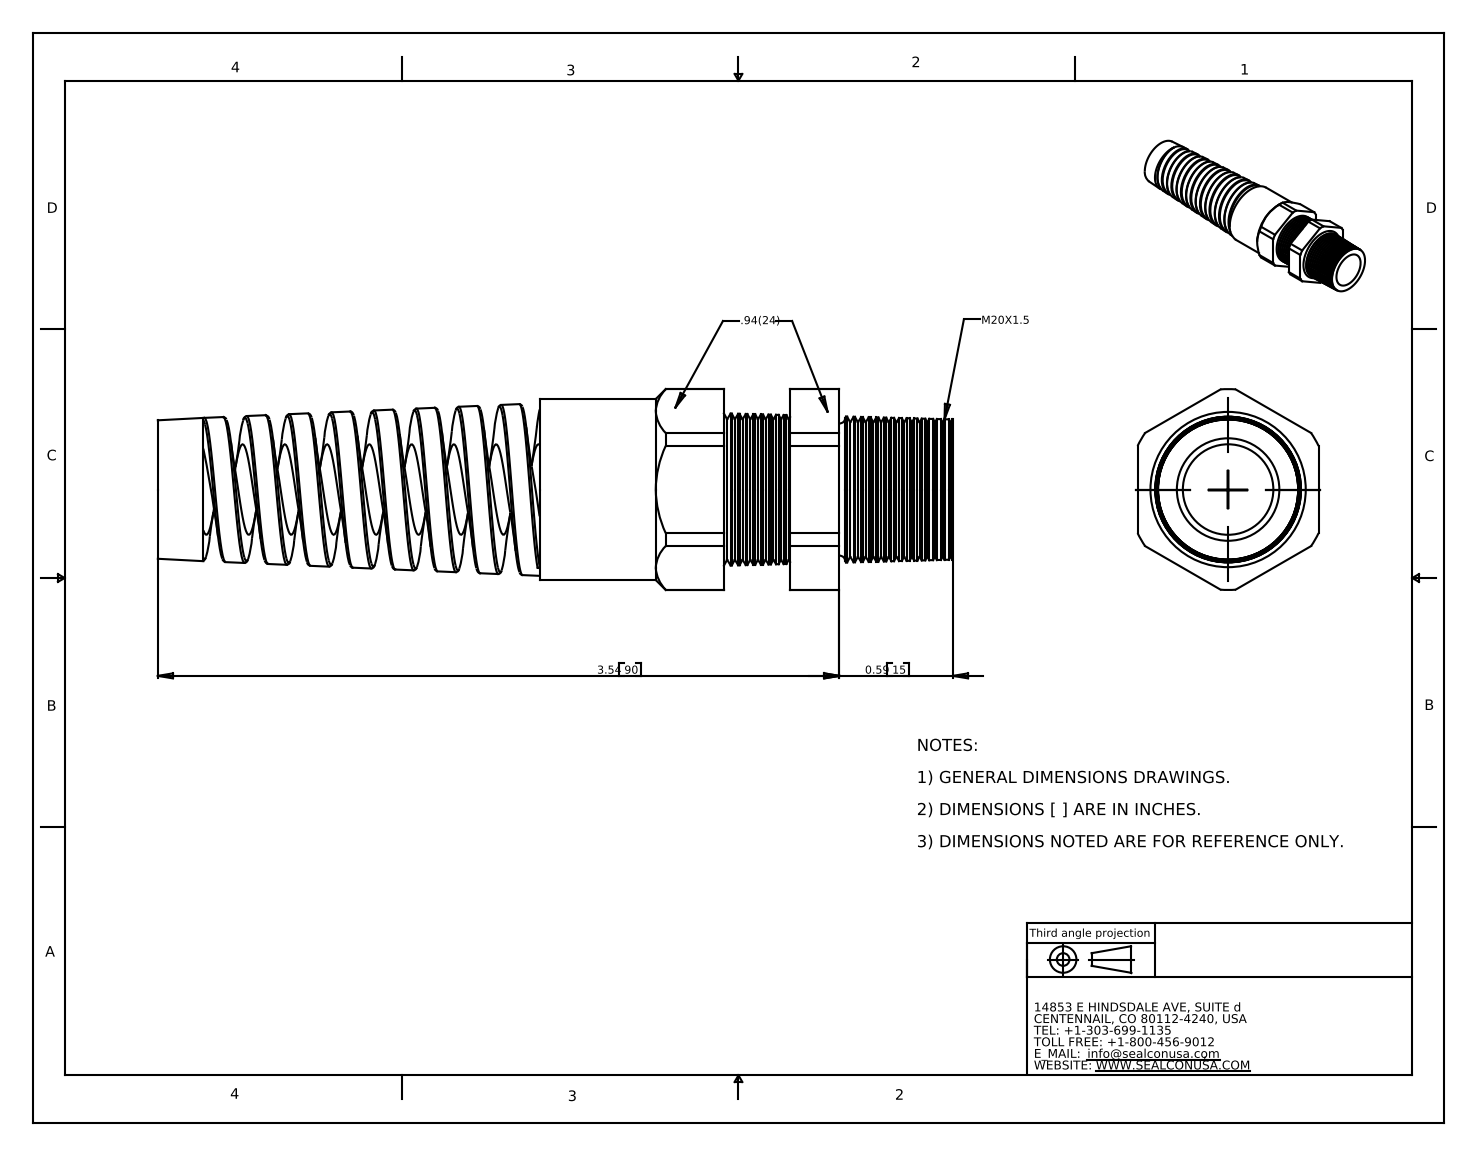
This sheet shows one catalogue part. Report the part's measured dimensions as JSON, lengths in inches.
{"part_name": "CF20DR-BK", "step_written_by": "SolidWorks 2007 (CONFIG_CONTROL_DESIGN)", "units": "inches", "bodies": {"solids": 2, "faces": 248, "planar": 25, "cylindrical": 41, "other": 182}, "overall_size": [4.13, 1.043, 0.94], "volume_in3": 1.312, "surface_area_in2": 23.79, "round_holes": [[0.47, 1], [0.495, 1]], "round_bosses_or_shafts": [[0.94, 1], [0.686, 1]], "partial_cylinders_radius": [[0.522, 1]], "face_to_face_distances": [0.94, 0.344, 0.6, 0.256, 0.957, 1.301, 1.557, 0.603, 0.354, 0.698]}
